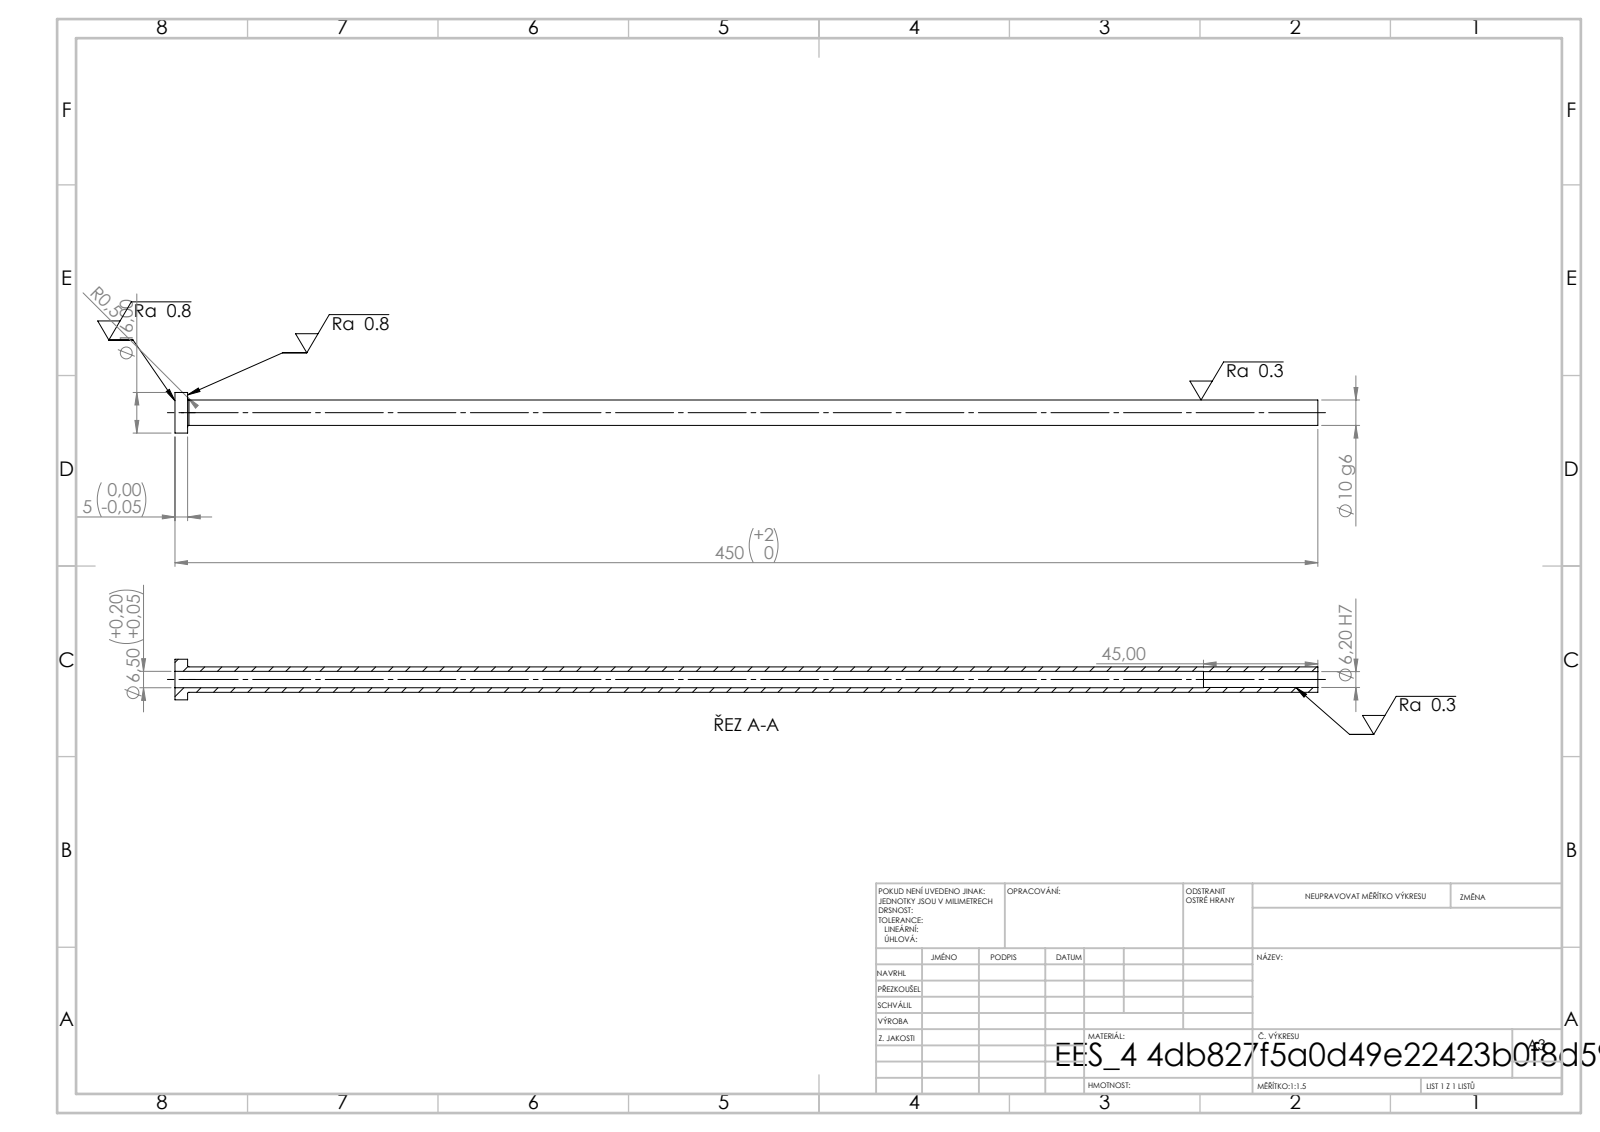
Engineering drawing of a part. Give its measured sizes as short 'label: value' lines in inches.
written by: SolidWorks 2019 (CONFIG_CONTROL_DESIGN)
unit: in
bodies: 1 solid, 14 faces (4 planar, 8 cylindrical, 2 other)
size: 17.717 × 0.63 × 0.63
volume: 1.291 in³; area: 36.76 in²
holes: 1× ⌀0.244, 1× ⌀0.256
bosses: 1× ⌀0.63, 1× ⌀0.394
face distances: 0.197, 17.717, 17.52, 15.945, 15.748, 1.772
